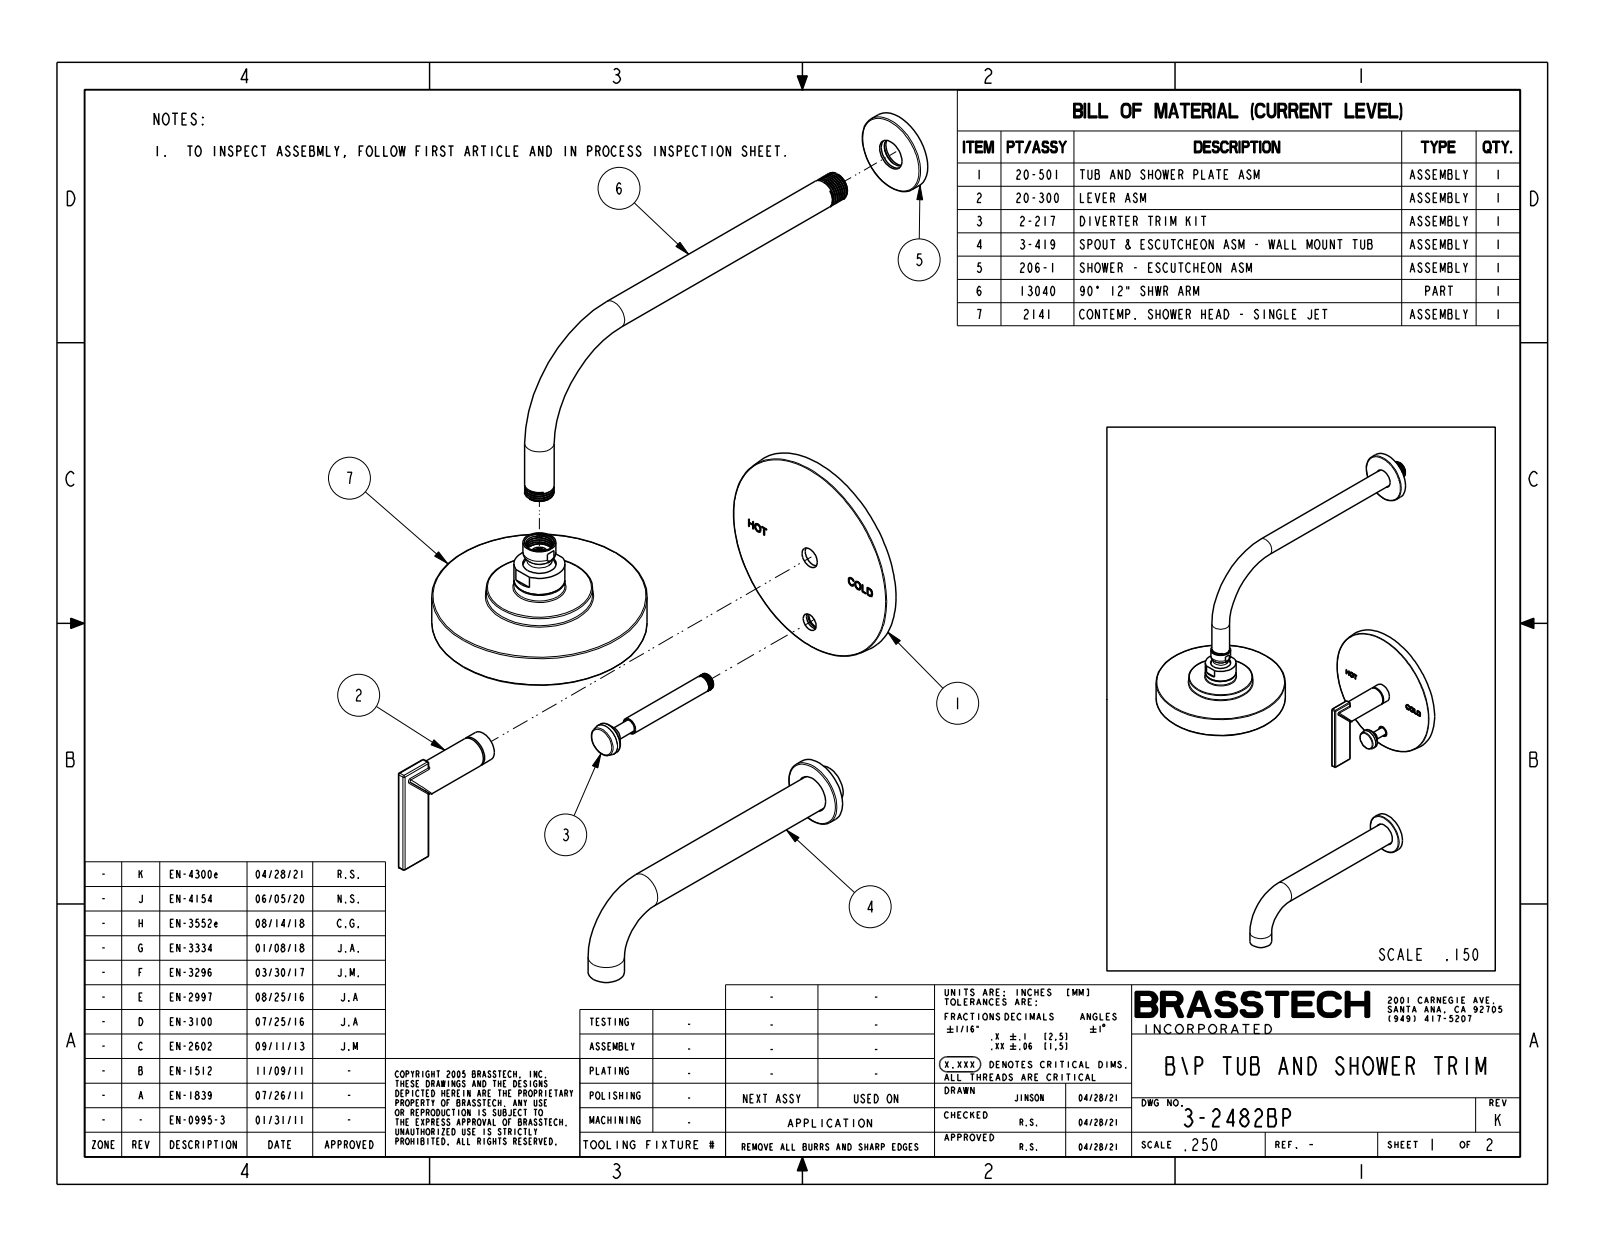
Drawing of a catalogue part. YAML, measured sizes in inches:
part_name: "3-2482BP"
step_written_by: "CREO PARAMETRIC BY PTC INC, 2018400 (CONFIG_CONTROL_DESIGN)"
units: inches
bodies: {solids: 3, faces: 1056, planar: 168, cylindrical: 236, other: 652}
overall_size: [23.125, 13.799, 6]
volume: 62.95
surface_area: 247.2
round_holes:
  - {diameter: 0.05, count: 90}
  - {diameter: 0.22, count: 1}
  - {diameter: 5.256, count: 1}
round_bosses_or_shafts:
  - {diameter: 1, count: 2}
  - {diameter: 0.813, count: 2}
  - {diameter: 5.91, count: 1}
  - {diameter: 5.22, count: 1}
  - {diameter: 2.92, count: 1}
  - {diameter: 2.25, count: 1}
  - {diameter: 1.85, count: 1}
  - {diameter: 1.4, count: 1}
partial_cylinders:
  - {radius: 0.04, count: 16}
face_to_face_distances: [0.35, 0.291, 0.31, 0.04, 0.236, 0.1, 0.25, 0.06, 1.084, 0.793]
hole_center_spacings: [0.98, 1.41, 0.55, 0.851, 1.893, 0.43, 0.476, 0.912]
